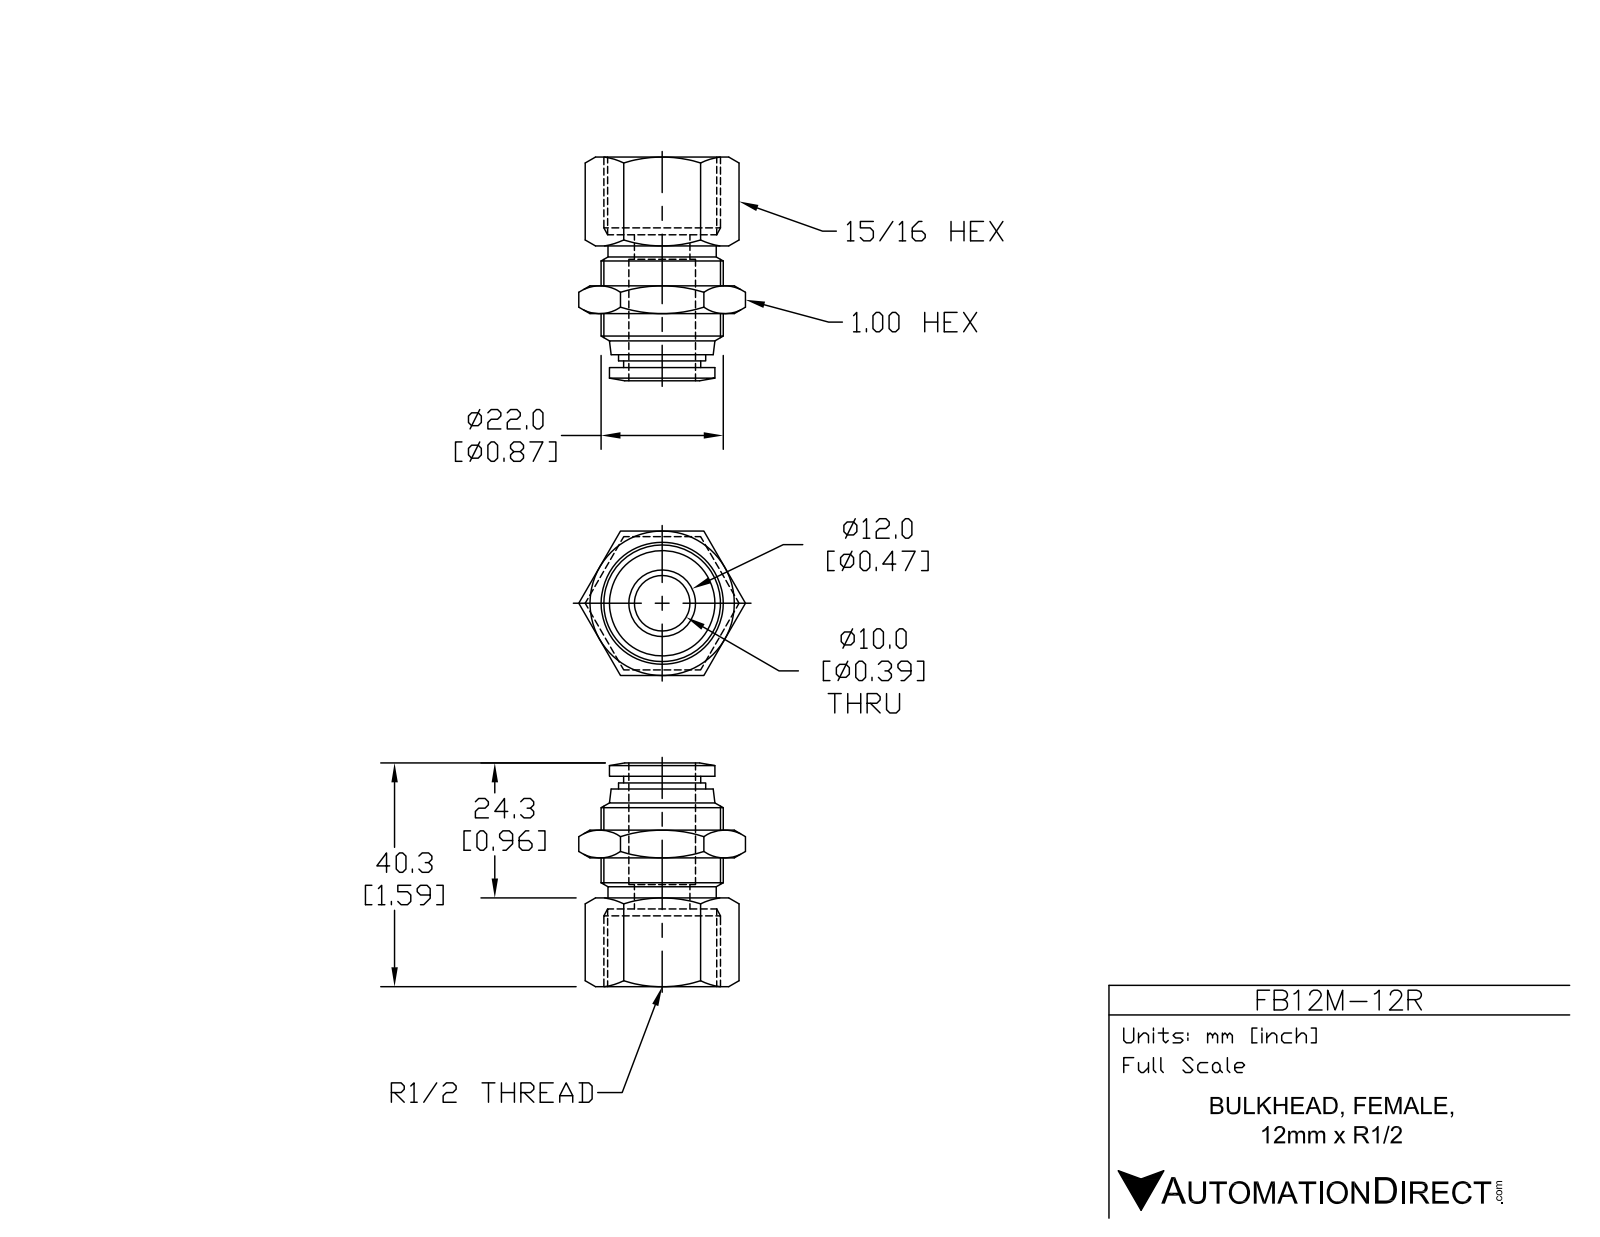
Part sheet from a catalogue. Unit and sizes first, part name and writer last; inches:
Units: inches
Overall size (bounding box): 1.587 × 1.182 × 1.024
Round holes (diameter × count): ⌀0.394 ×1, ⌀0.484 ×1
Round bosses / shafts (diameter × count): ⌀0.866 ×1, ⌀0.768 ×1, ⌀0.748 ×1, ⌀0.618 ×1, ⌀0.547 ×1
Main face-to-face distances: 0.945, 0.039, 0.984, 1.024, 0.079, 0.559, 0.48, 0.362, 0.283, 0.197
Volume: 0.571 in³ · Surface area: 9.769 in²
Bodies: 1 solid, 78 faces (22 planar, 16 cylindrical, 40 other)
Part name (STEP PRODUCT): FB12M-12R
STEP written by: SolidWorks 2015 (AUTOMOTIVE_DESIGN)
